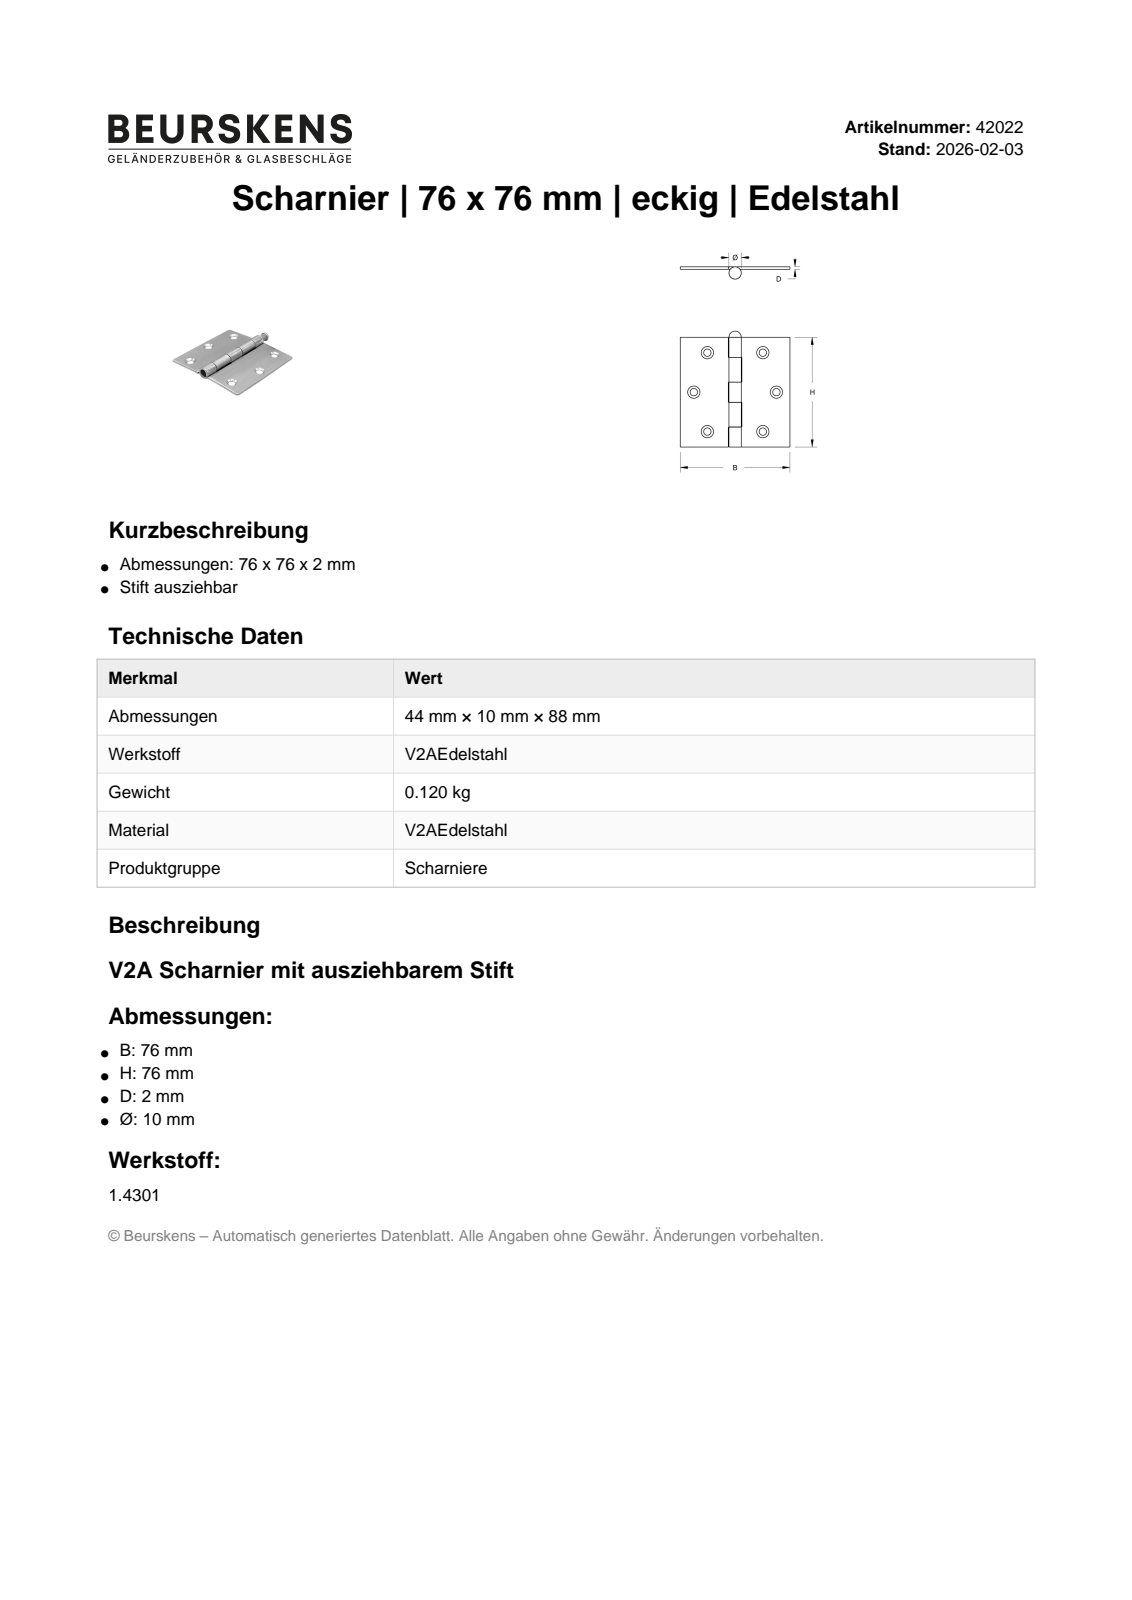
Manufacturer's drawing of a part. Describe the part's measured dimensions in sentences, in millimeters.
The part is named "420223; 42022-01; 42022-02; 42022-03". Its 3-D file was written by "Autodesk Inventor 2023 (AUTOMOTIVE_DESIGN)". It is 3 solids with 52 faces: 26 planar, 18 cylindrical and 8 other. Overall it measures 81 by 76 by 10.5 millimeters. Its volume is 16 371 cubic millimeters and its surface area 17 043 square millimeters. Round holes: 6 of diameter 6, 1 of diameter 6.2. Round bosses or shafts: 1 of diameter 10.5, 1 of diameter 9, 1 of diameter 6. The main face-to-face distances are 34, 76, 30, 46, 12, 64, 18, 42, 52, 16. The hole center spacings are 29.61, 58.
